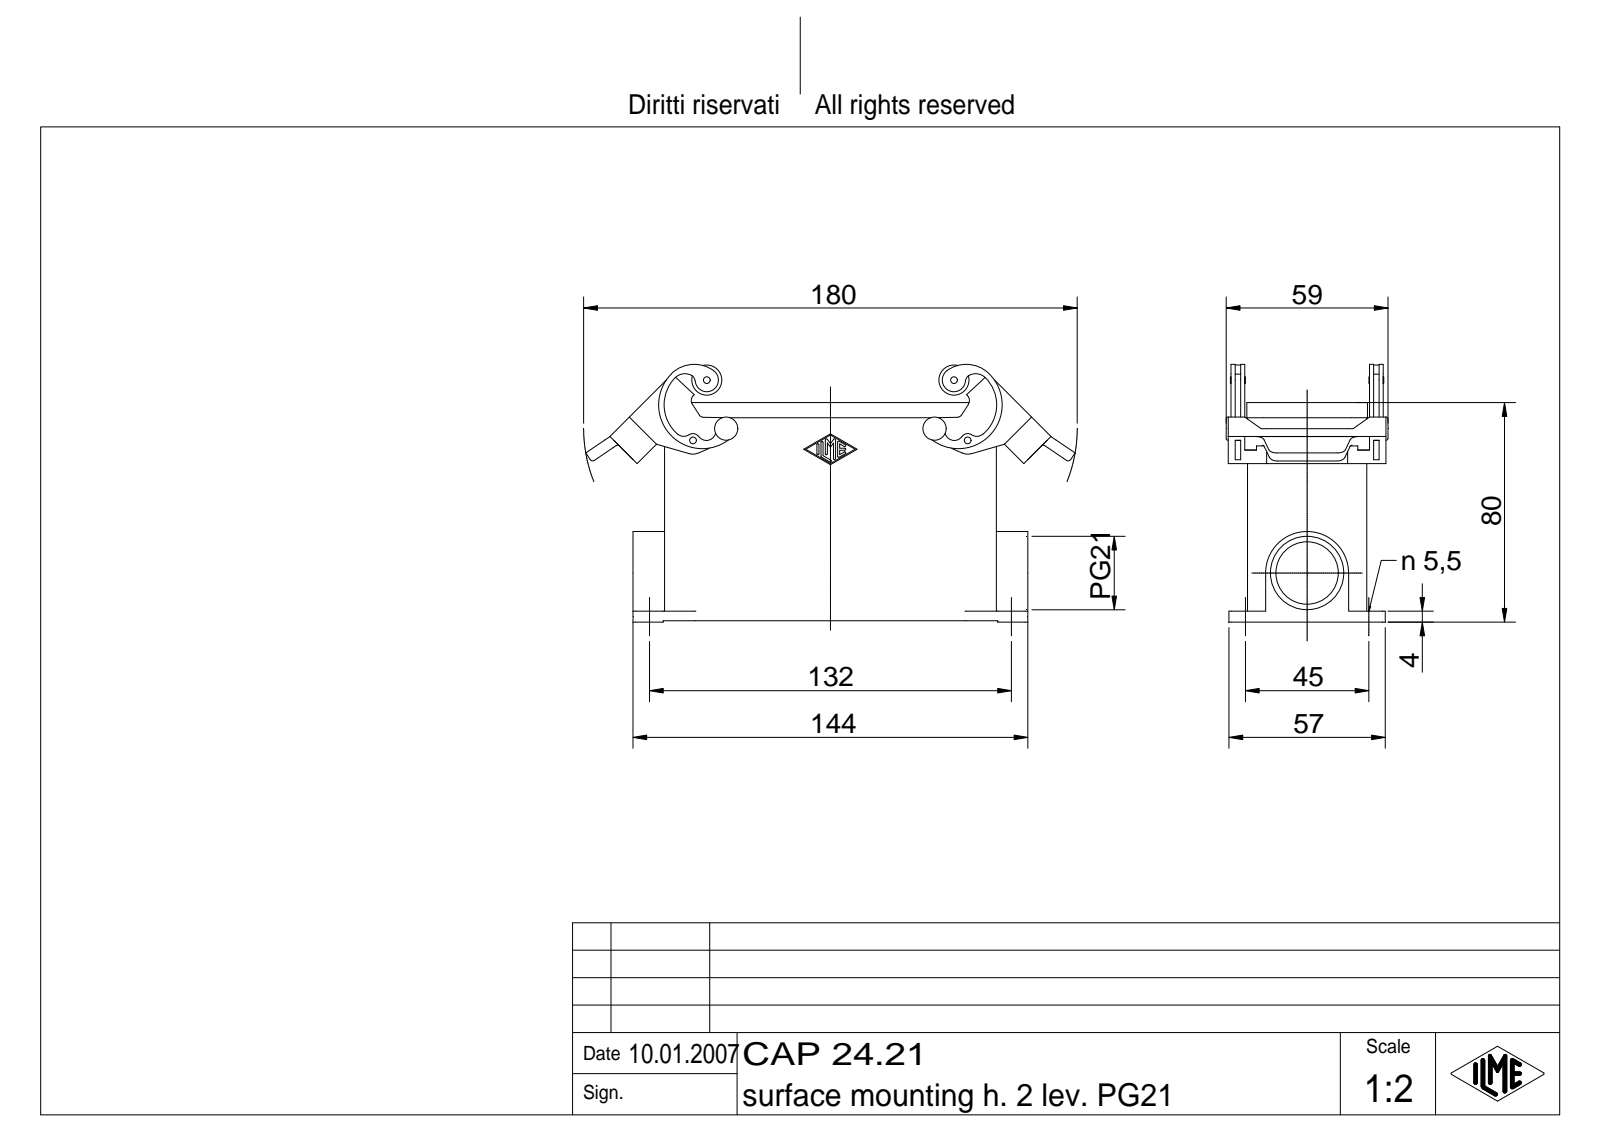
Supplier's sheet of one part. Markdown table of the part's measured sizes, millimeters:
| quantity | value |
| --- | --- |
| part name | CAP 24.21 |
| STEP written by | Autodesk Inventor 7 (AUTOMOTIVE_DESIGN) |
| units | millimeters |
| bodies | 1 solid, 749 faces (191 planar, 205 cylindrical, 353 other) |
| overall size | 178.49 × 93.94 × 58 |
| volume | 146 602 mm³ |
| surface area | 81 249 mm² |
| round holes (diameter × count) | 2 × 4, 5.5 × 4, 2.5 × 2, 22.78 × 1, 26.78 × 1 |
| round bosses / shafts (diameter × count) | 11 × 2, 5 × 2, 3 × 2 |
| partial cylindrical surfaces (radius × count) | 1 × 20, 0.38 × 14, 3 × 12, 6 × 8, 2.5 × 6, 1.5 × 4, 2 × 4, 3.5 × 4 |
| main face-to-face distances | 3, 40.5, 43.5, 37.5, 3.5, 4, 0.75, 50.5, 40.75, 3.75 |
| hole center spacings | 22.56, 45, 97.67, 132, 139.46, 90.14, 100.18 |
